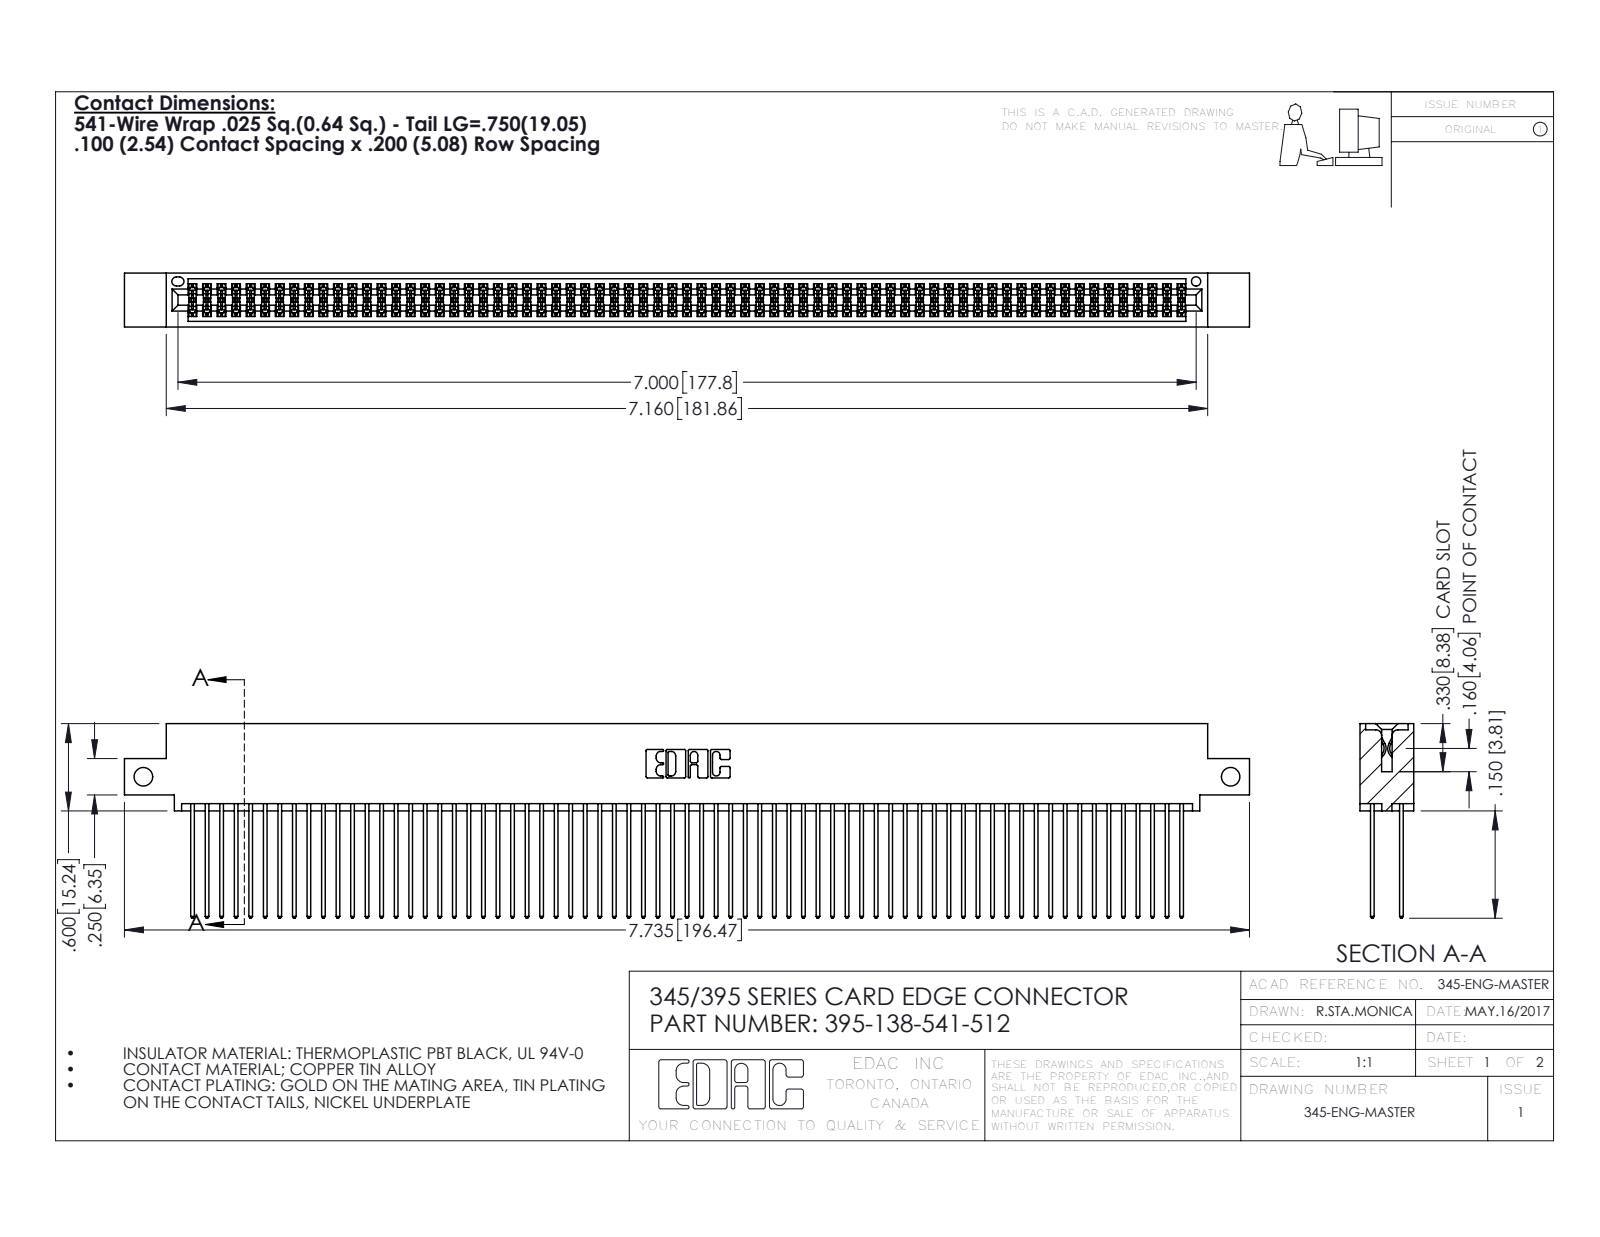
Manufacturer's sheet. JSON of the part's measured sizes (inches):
{"part_name": "345-292-001_345-293-141; 345 Part_0.110 Offset - Side Mount; 395-138-541-512", "step_written_by": "SolidWorks 2016 (CONFIG_CONTROL_DESIGN)", "units": "inches", "bodies": {"solids": 139, "faces": 7030, "planar": 4638, "cylindrical": 2392, "other": 0}, "overall_size": [7.735, 1.337, 0.37], "volume_in3": 1.218, "surface_area_in2": 52.26, "round_holes": [[0.128, 2], [0.064, 1]], "partial_cylinders_radius": [[0.006, 207], [0.01, 138], [0.01, 22], [0.007, 6], [0.031, 6], [0.026, 3], [0.014, 2], [0.019, 2]], "face_to_face_distances": [0.072, 0.298, 0.2, 0.098, 0.272, 0.025, 0.225, 0.37, 0.175, 0.149], "hole_center_spacings": [7.475]}
